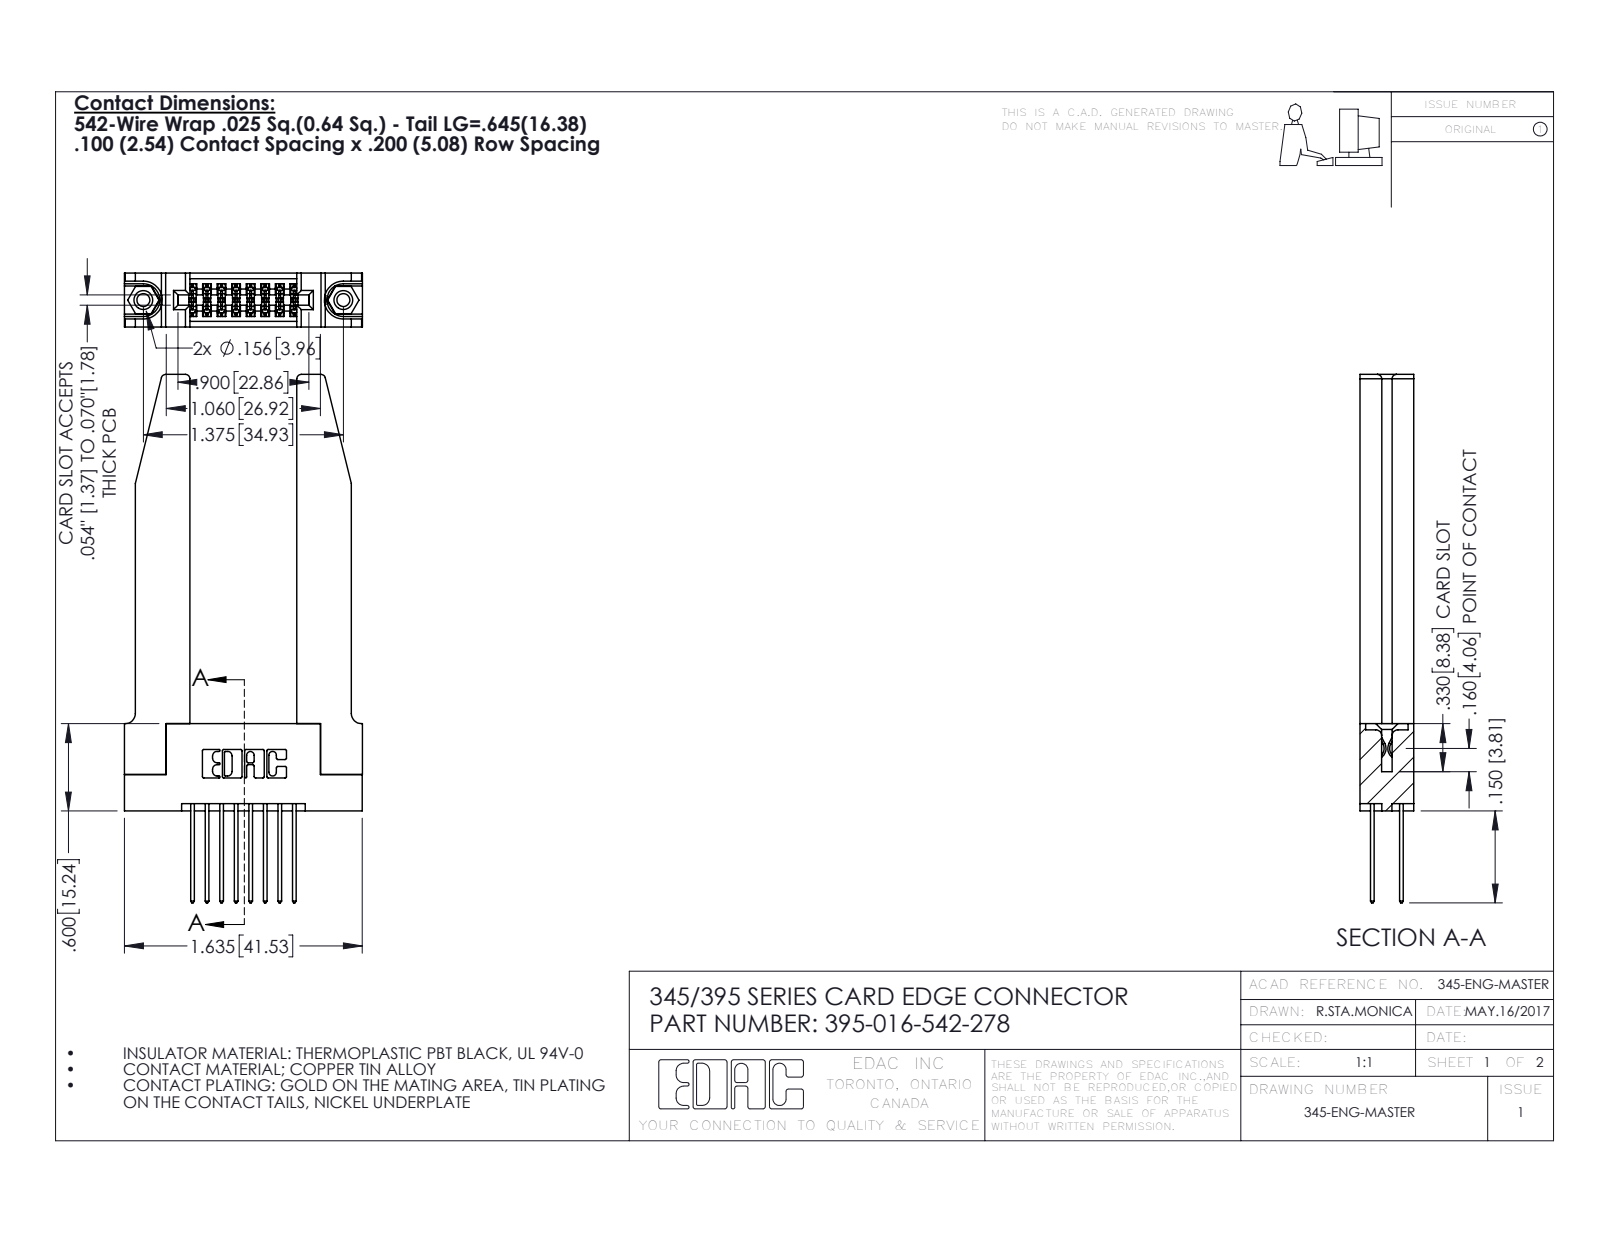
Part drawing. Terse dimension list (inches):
name: 345 Part_Flush Mounting Lugs - 0.156 Dia-TH; 345-292-001_345-293-142; 345-250-001_345-250-001-102; 395-016-542-278 (+1 more)
written by: SolidWorks 2016 (CONFIG_CONTROL_DESIGN)
unit: in
bodies: 21 solids, 1160 faces (750 planar, 358 cylindrical, 52 other)
size: 3.632 × 1.636 × 0.37
volume: 0.706 in³; area: 18.82 in²
holes: 2× ⌀0.089, 2× ⌀0.125, 2× ⌀0.156, 1× ⌀0.064
bosses: 2× ⌀0.155
rounds: 24× R0.006, 22× R0.01, 16× R0.01, 8× R0.03, 6× R0.007, 6× R0.031, 3× R0.026, 2× R0.014
face distances: 0.37, 0.072, 0.298, 0.2, 0.148, 0.15, 0.077, 0.22, 0.735, 0.098
hole spacings: 0.27, 1.144, 1.375
